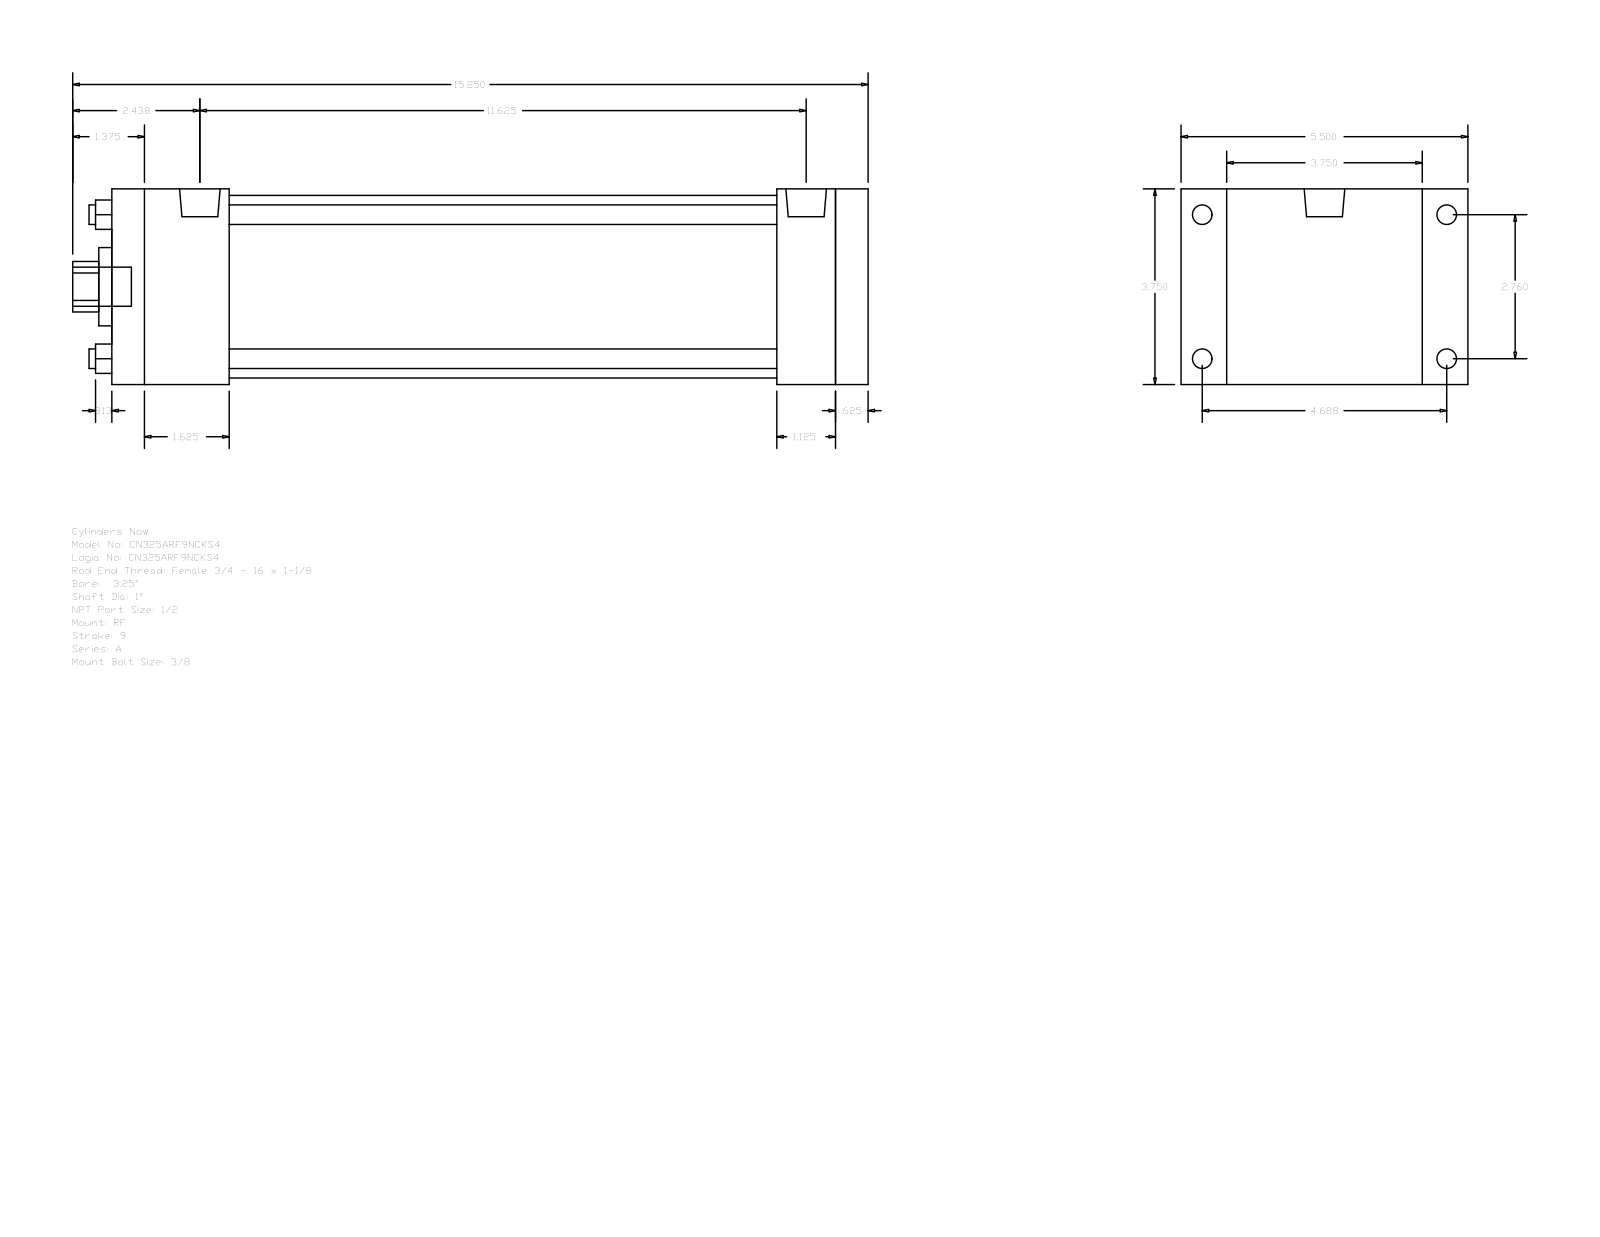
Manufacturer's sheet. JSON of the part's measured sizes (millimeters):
{"part_name": "A_RF__0325_1", "step_written_by": "GSSL Pune (CONFIG_CONTROL_DESIGN)", "units": "millimeters", "bodies": {"solids": 0, "faces": 92, "planar": 64, "cylindrical": 28, "other": 0}, "overall_size": [387.35, 139.7, 95.25], "round_holes": [[9.53, 4], [25.4, 1], [38.1, 1], [88.9, 1]], "round_bosses_or_shafts": [[9.53, 4], [8.73, 4], [19.77, 2], [19.05, 1]], "partial_cylinders_radius": [[12.29, 1]], "face_to_face_distances": [95.24, 368.3, 15.87, 352.43, 22.23, 117.47, 323.85, 28.58, 44.45, 57.15], "hole_center_spacings": [49.57, 70.1, 99.14]}
